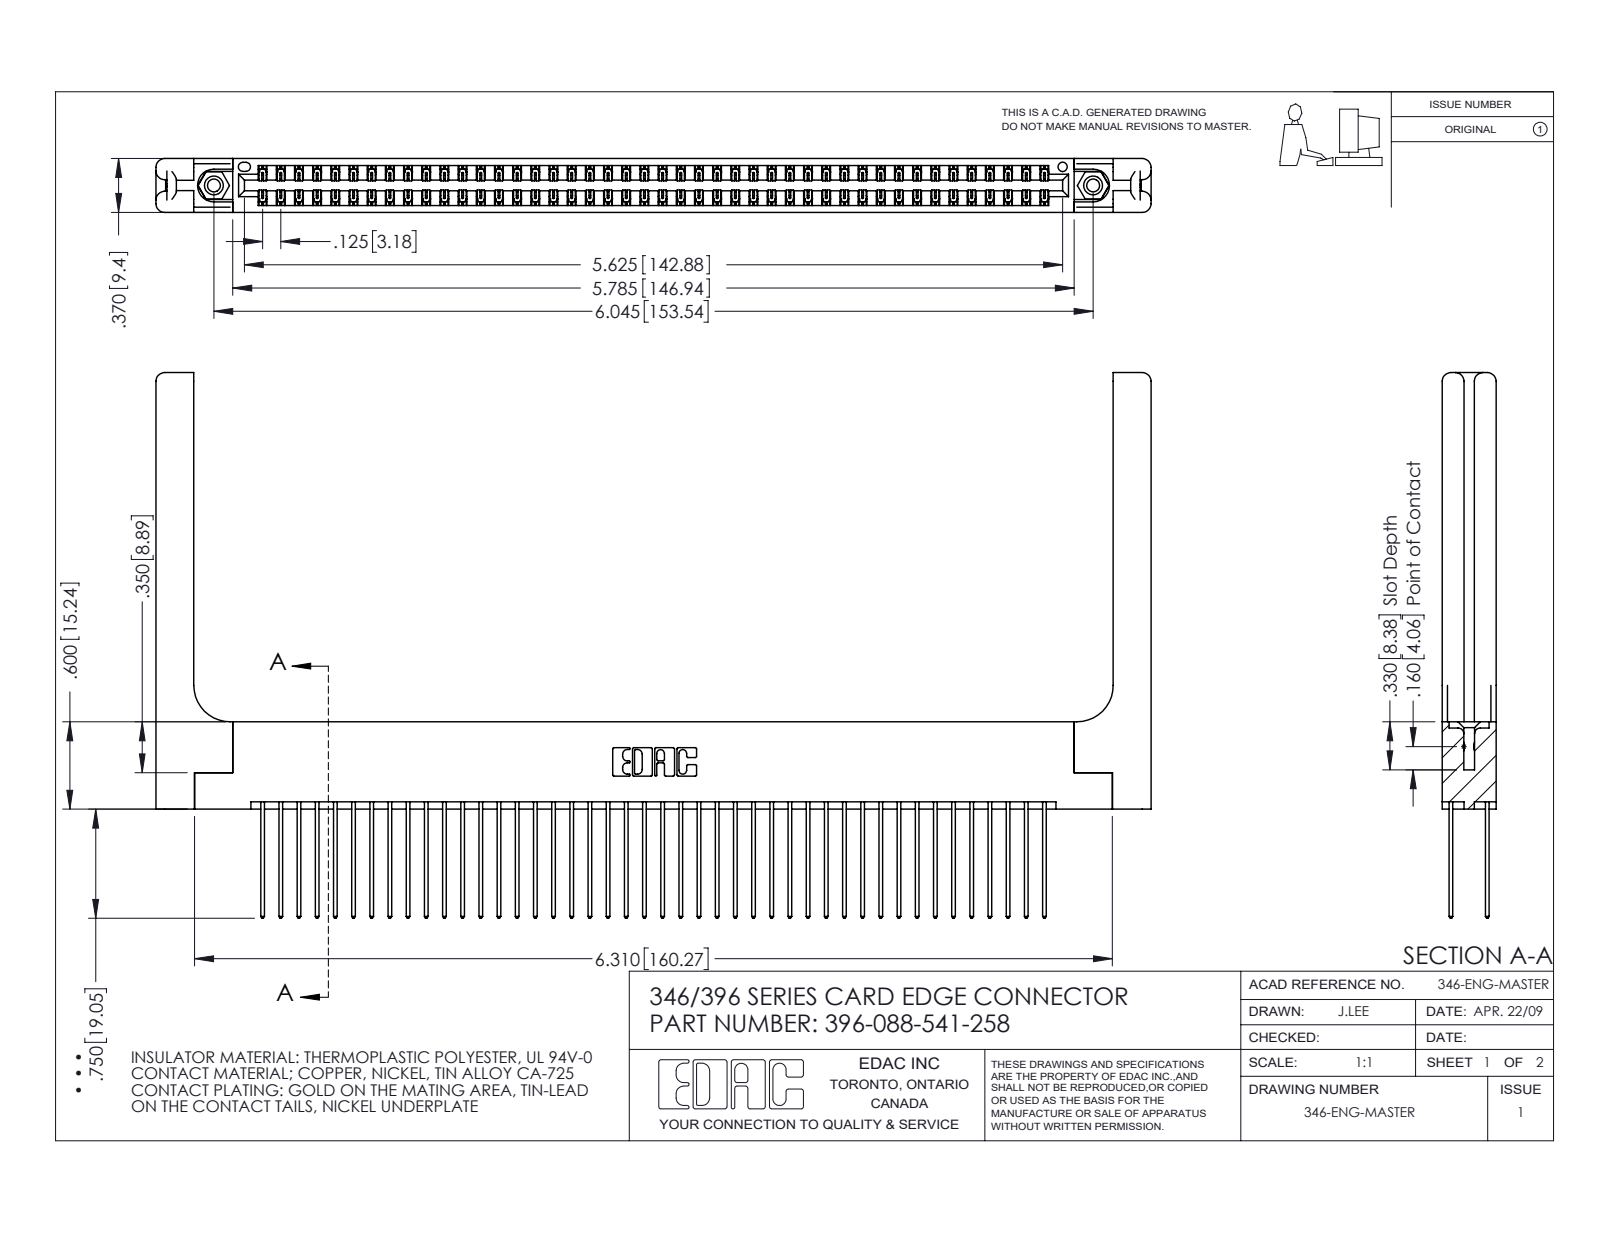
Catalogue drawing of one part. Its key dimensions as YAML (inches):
part_name: "396-088-541-258; 345-292-001_345-293-141; 346-220-058_345-220-058; 346 Part_Flush Mounting Lugs - 0.156 Dia-TH (+1 more)"
step_written_by: "SolidWorks 2016 (CONFIG_CONTROL_DESIGN)"
units: inches
bodies: {solids: 93, faces: 4954, planar: 3304, cylindrical: 1590, other: 60}
overall_size: [6.841, 3.75, 0.37]
volume: 1.523
surface_area: 48.72
round_holes:
  - {diameter: 0.089, count: 2}
  - {diameter: 0.125, count: 2}
  - {diameter: 0.156, count: 2}
  - {diameter: 0.064, count: 1}
round_bosses_or_shafts:
  - {diameter: 0.155, count: 2}
partial_cylinders:
  - {radius: 0.006, count: 132}
  - {radius: 0.01, count: 88}
  - {radius: 0.01, count: 22}
  - {radius: 0.06, count: 16}
  - {radius: 0.007, count: 6}
  - {radius: 0.031, count: 6}
  - {radius: 0.026, count: 3}
  - {radius: 0.014, count: 2}
face_to_face_distances: [0.048, 0.322, 0.072, 0.37, 0.25, 0.025, 0.298, 0.275, 0.148, 0.15]
hole_center_spacings: [0.246, 5.836, 6.045]
